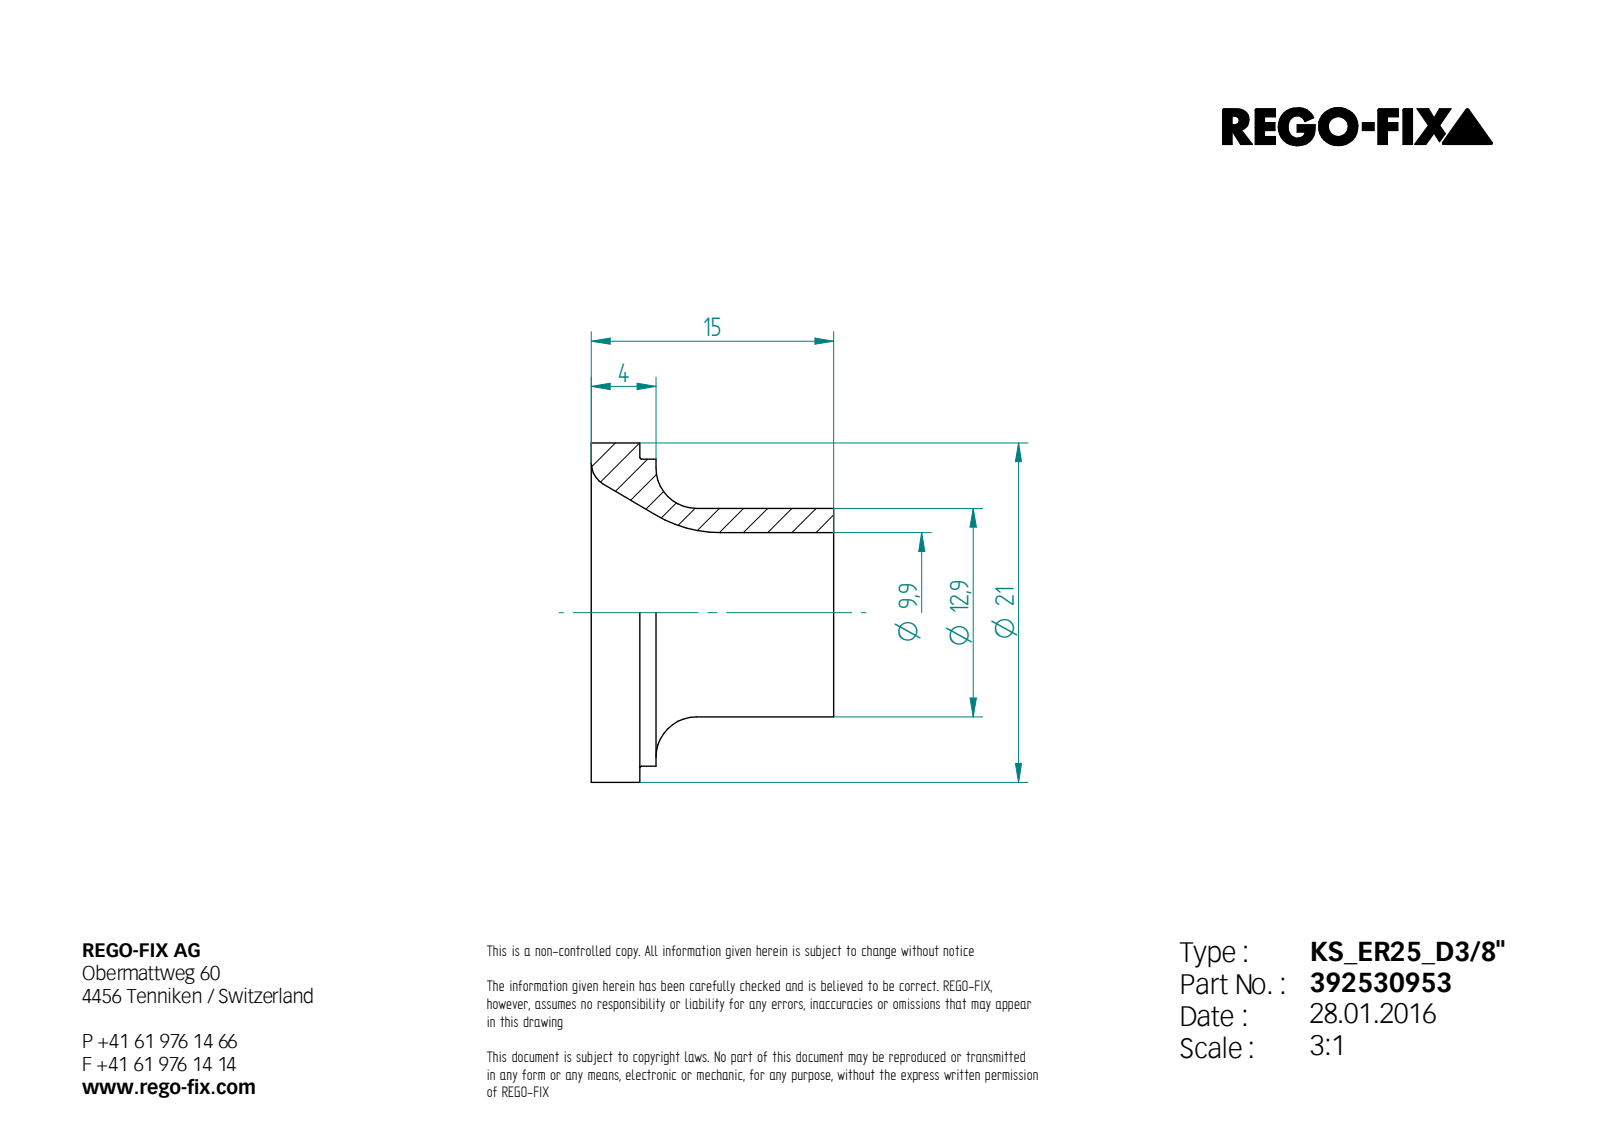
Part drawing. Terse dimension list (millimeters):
written by: Unknown (AUTOMOTIVE_DESIGN)
unit: mm
bodies: 1 solid, 13 faces (4 planar, 4 cylindrical, 5 other)
size: 21 × 21 × 15
volume: 1 262 mm³; area: 1 615 mm²
holes: 1× ⌀9.9
bosses: 1× ⌀21, 1× ⌀19, 1× ⌀12.9
face distances: 3, 15, 12, 4, 1, 11
